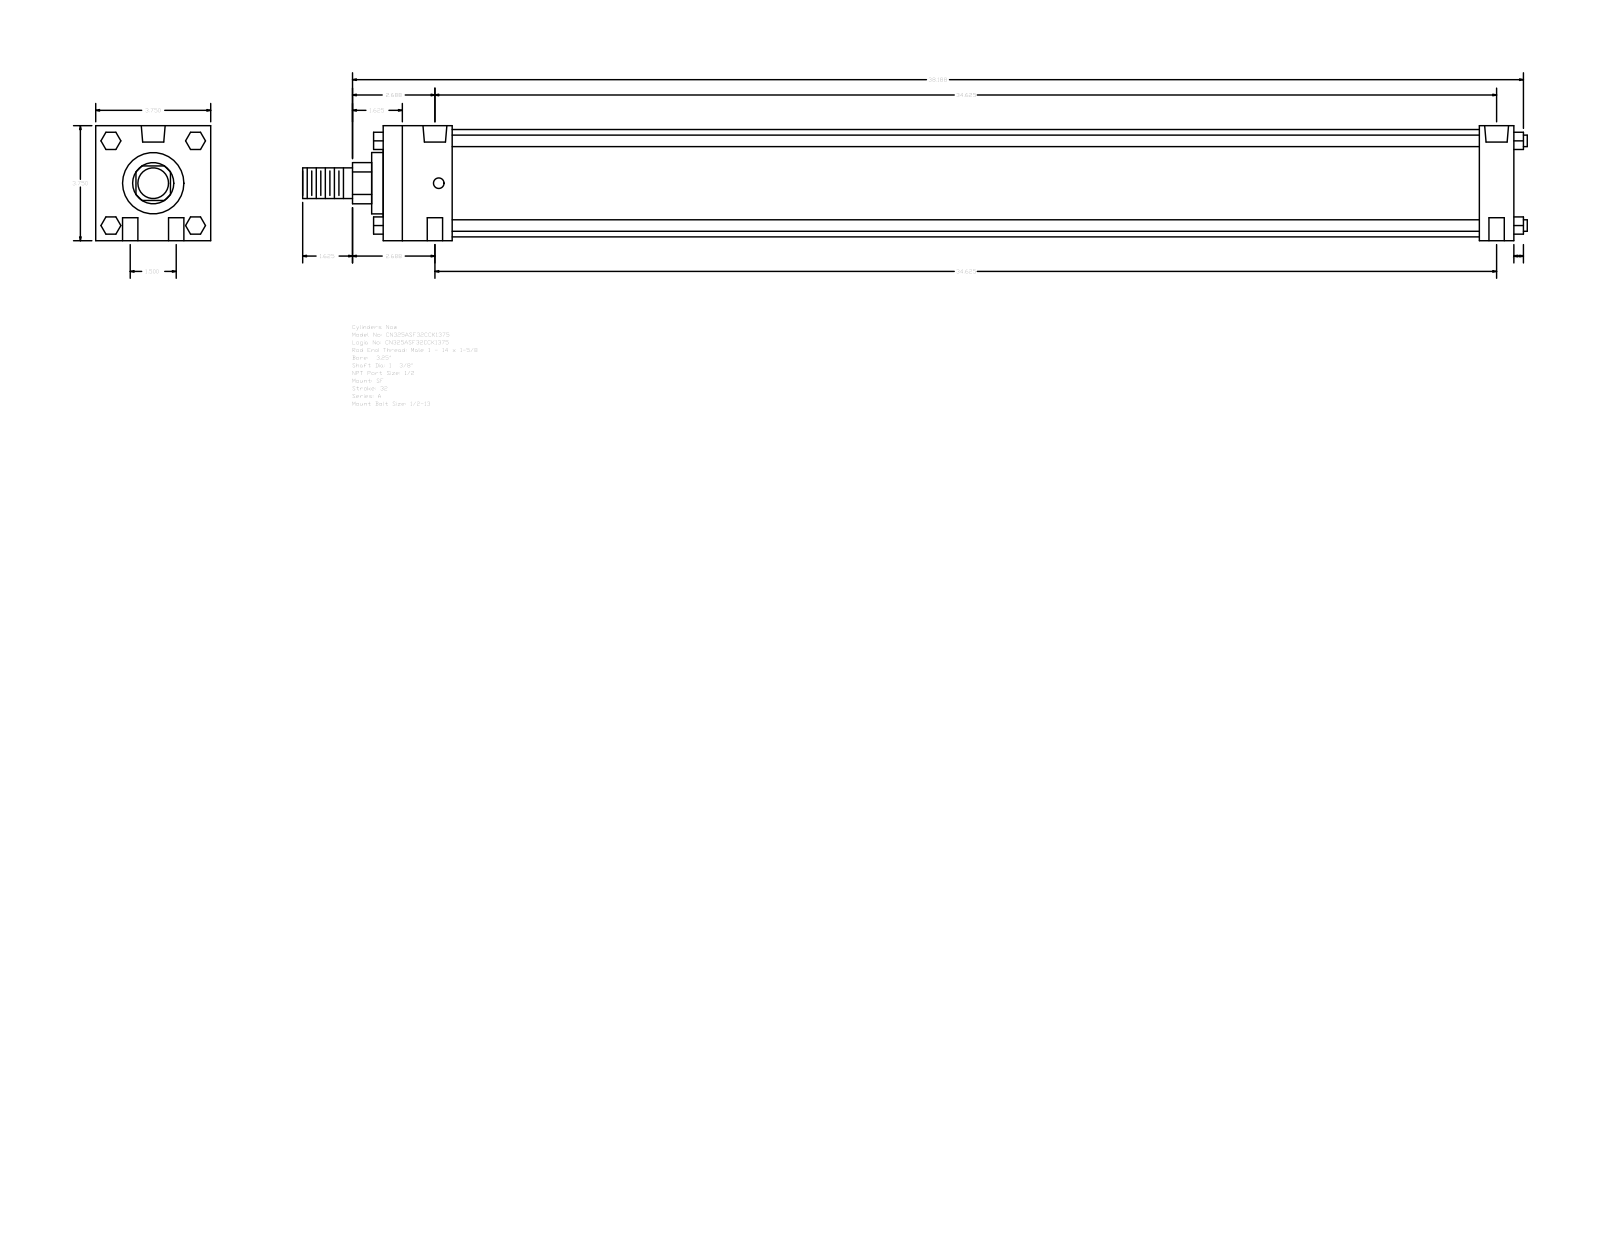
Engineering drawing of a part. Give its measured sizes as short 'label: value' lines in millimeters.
name: A_SF__0325_1.375
written by: GSSL Pune (CONFIG_CONTROL_DESIGN)
unit: mm
bodies: 0 solids, 124 faces (94 planar, 30 cylindrical, 0 other)
size: 1014.41 × 95.25 × 95.25
holes: 4× ⌀12.7, 2× ⌀8.73, 2× ⌀19.77
bosses: 4× ⌀9.53, 1× ⌀88.9, 1× ⌀50.8, 1× ⌀34.92, 1× ⌀25.4
rounds: 1× R17.06
face distances: 95.24, 936.62, 57.15, 908.05, 28.57, 850.9, 879.47, 66.67, 9.52, 917.57
hole spacings: 19.05, 879.69, 879.48, 38.1, 880.3, 873.12
